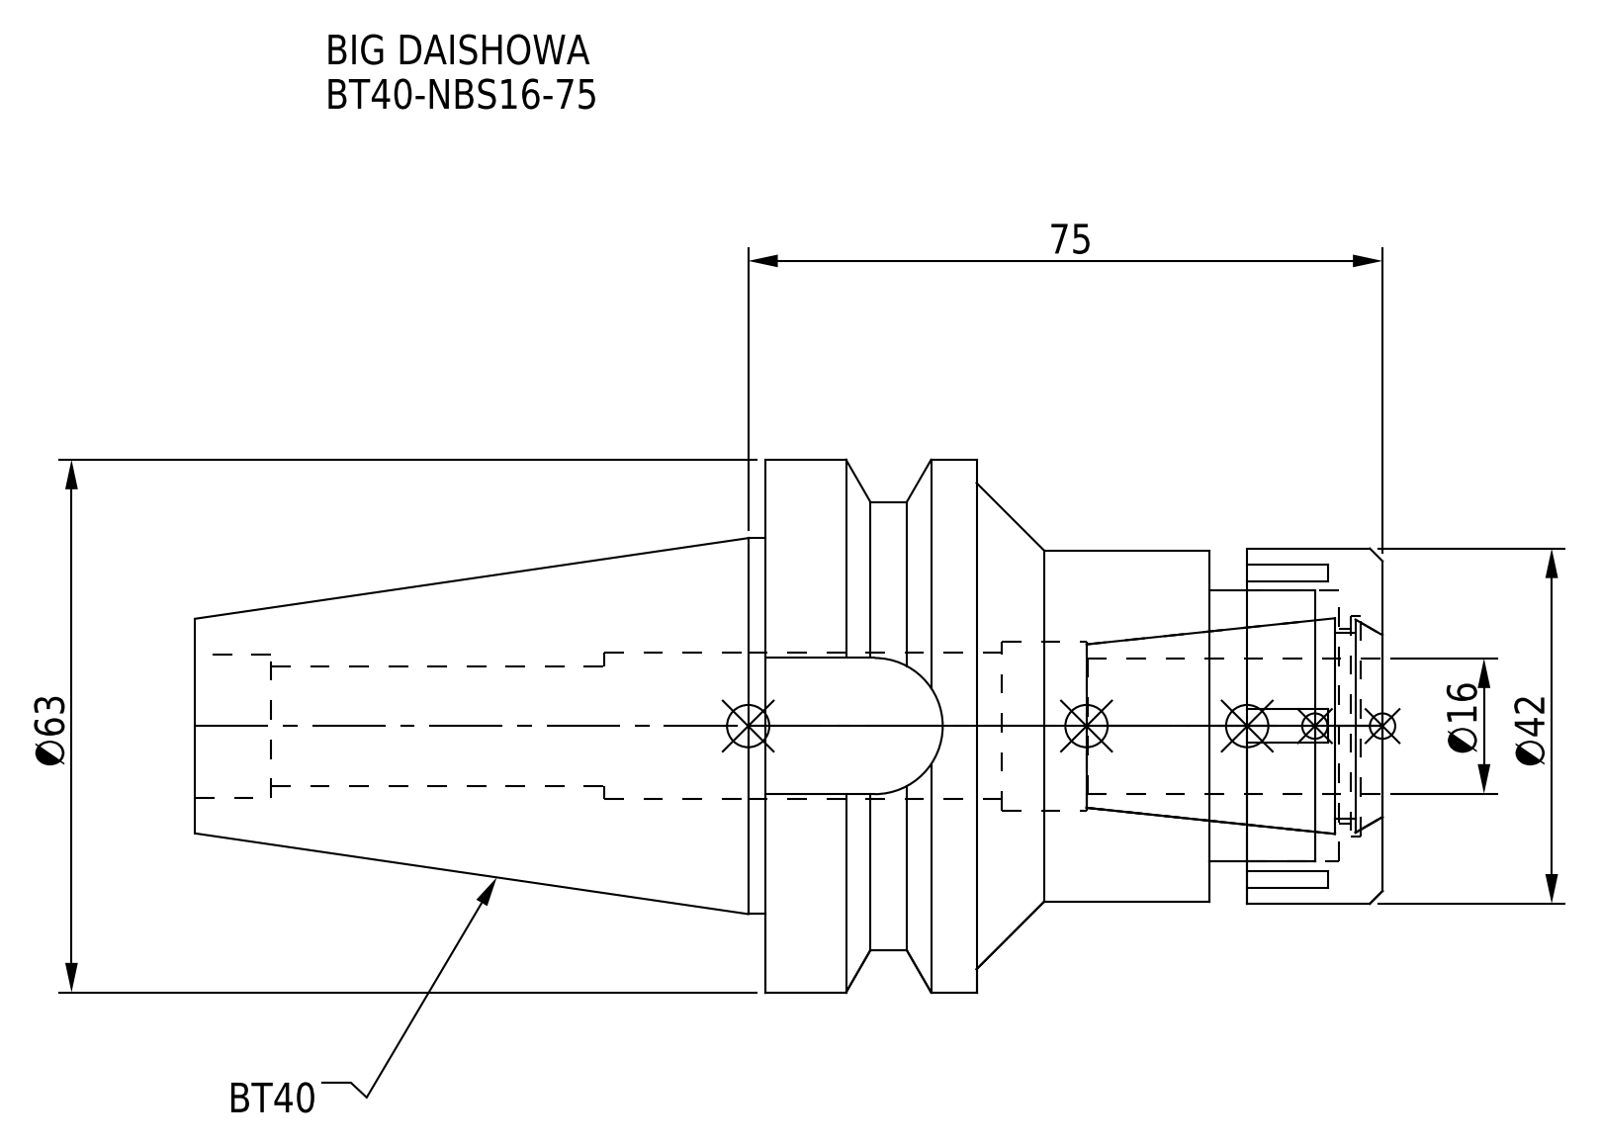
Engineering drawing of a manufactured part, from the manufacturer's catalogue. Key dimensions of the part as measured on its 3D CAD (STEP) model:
Part name (STEP PRODUCT): BT40-NBS16-75.stp; BT40-NBS16-75; BT40-NBS16-75_1.stp; NBN16_1.stp (+3 more)
STEP written by: SolidWorks 2019 (CONFIG_CONTROL_DESIGN)
Units: millimetres
Bodies: 2 solids, 90 faces (44 planar, 32 cylindrical, 14 other)
Overall size (bounding box): 140.4 × 63 × 63
Volume: 163 780 mm³ · Surface area: 35 810 mm²
Round holes (diameter × count): ⌀14.2 ×1, ⌀17 ×1, ⌀17.3 ×1, ⌀20 ×1, ⌀23 ×1, ⌀26 ×1, ⌀32 ×1
Round bosses / shafts (diameter × count): ⌀63 ×1, ⌀53 ×1, ⌀44.45 ×1, ⌀42 ×1, ⌀41.5 ×1
Partial cylindrical surfaces — rounded edges, fillets, slot ends (radius × count): R8.05 ×1
Main face-to-face distances: 73, 8, 20.5, 52.5, 57, 16, 4.5, 48, 32, 27.5
